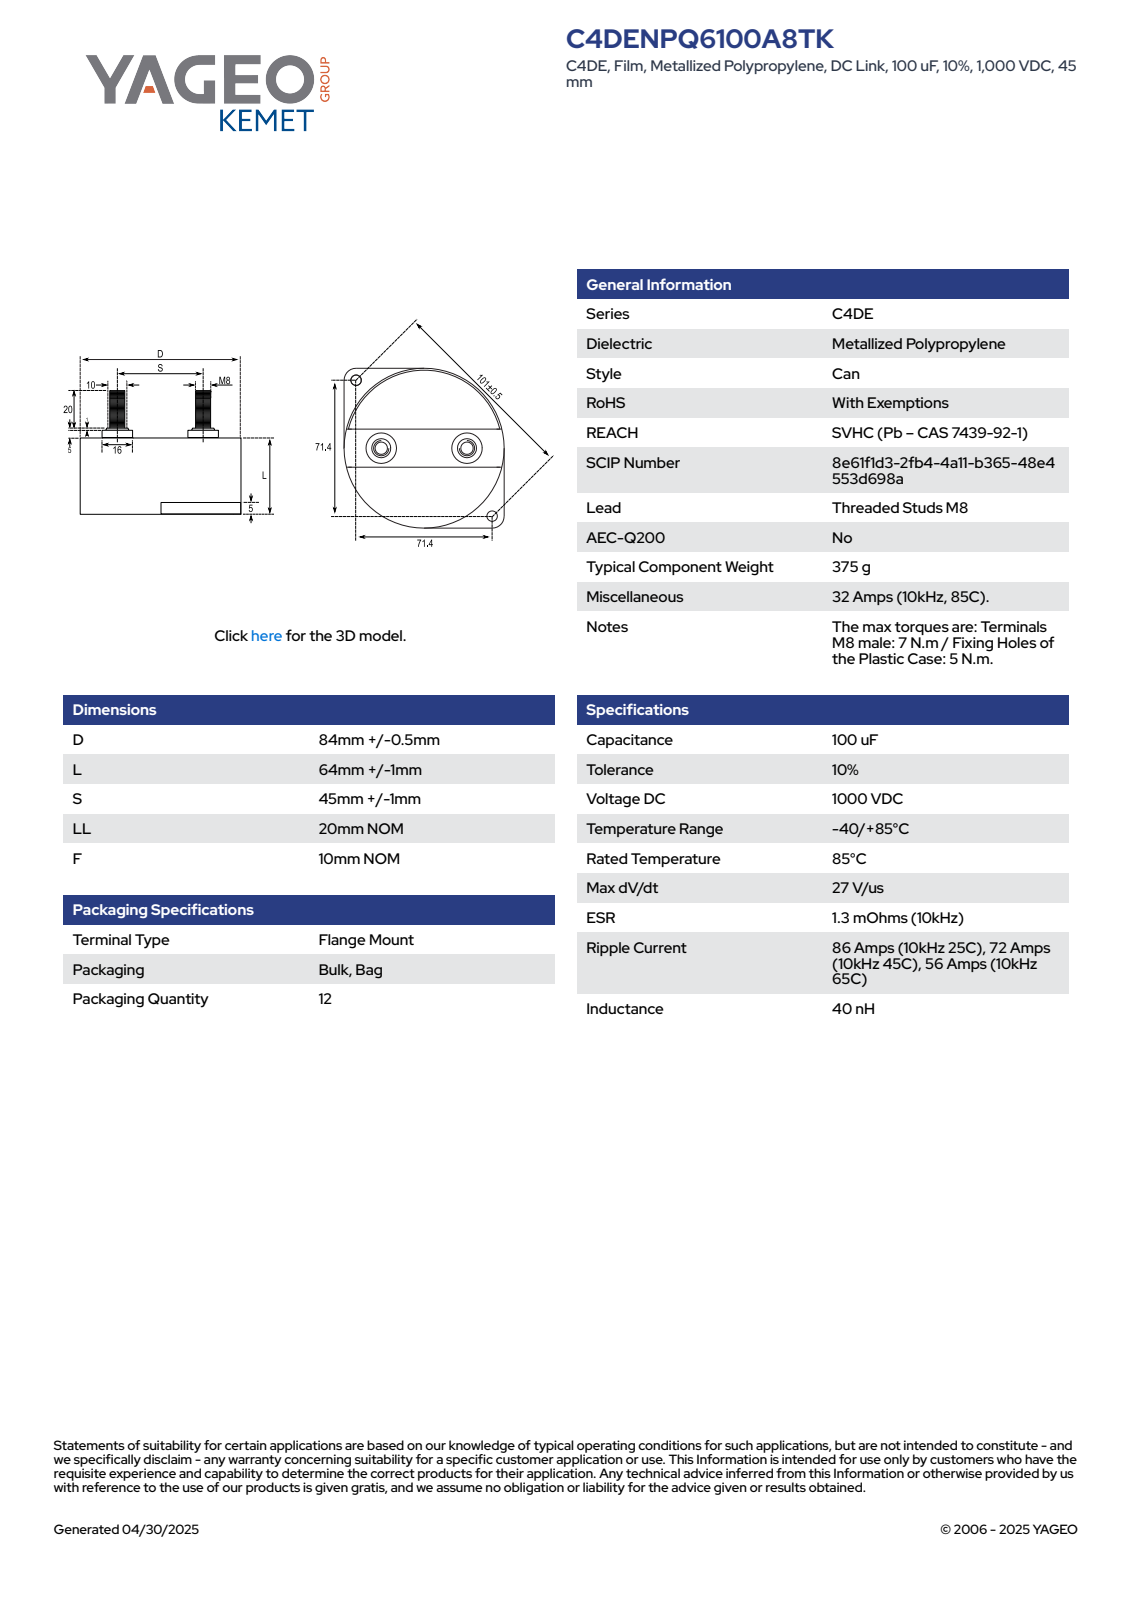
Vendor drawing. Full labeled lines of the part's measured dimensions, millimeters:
Part name (STEP PRODUCT): CFP_C44DE_84X64_D84.5L66S46LL20
STEP written by: SolidWorks 2014 (AUTOMOTIVE_DESIGN)
Units: millimetres
Bodies: 1 solid, 103 faces (37 planar, 31 cylindrical, 35 other)
Overall size (bounding box): 92 × 84.51 × 84.5
Volume: 377 698 mm³ · Surface area: 31 954 mm²
Round holes (diameter × count): ⌀5.5 ×2
Round bosses / shafts (diameter × count): ⌀16 ×2, ⌀10 ×2, ⌀8 ×2, ⌀84.5 ×1, ⌀80 ×1
Partial cylindrical surfaces — rounded edges, fillets, slot ends (radius × count): R10 ×2, R42.26 ×1
Main face-to-face distances: 66.01, 5, 66, 61.01, 61, 84.5, 71, 4.99, 92, 87
Hole centre spacings: 101.51
